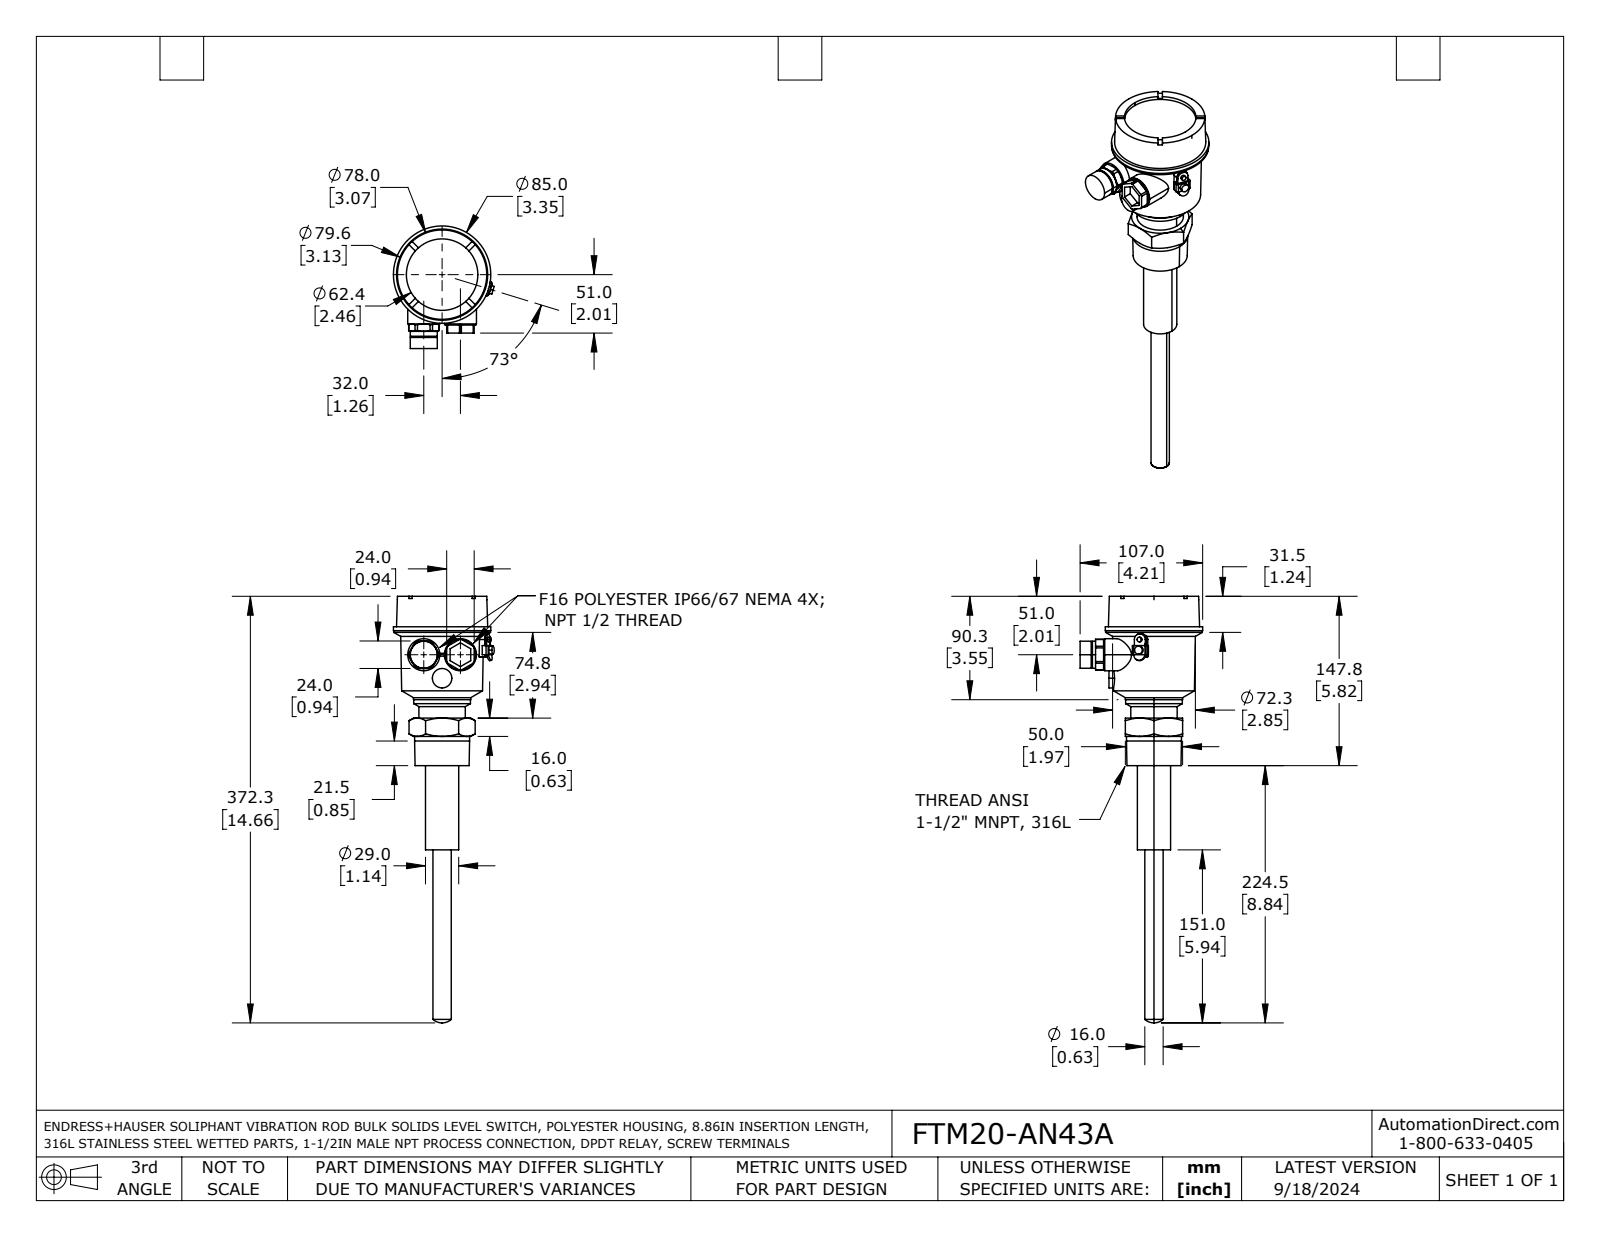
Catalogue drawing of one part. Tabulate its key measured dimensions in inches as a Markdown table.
| quantity | value |
| --- | --- |
| part name | FTM20-AN43A |
| STEP written by | SolidWorks 2021 (AUTOMOTIVE_DESIGN) |
| units | inches |
| bodies | 1 solid, 223 faces (113 planar, 56 cylindrical, 54 other) |
| overall size | 14.657 × 4.213 × 3.464 |
| volume | 35.84 in³ |
| surface area | 94.94 in² |
| round holes (diameter × count) | 2.457 × 1 |
| round bosses / shafts (diameter × count) | 1.102 × 2, 3.346 × 1, 3.327 × 1, 1.969 × 1, 1.949 × 1, 1.89 × 1, 1.594 × 1, 1.142 × 1 |
| partial cylindrical surfaces (radius × count) | 0.059 × 3, 0.197 × 1, 0.52 × 1 |
| main face-to-face distances | 0.118, 1.969, 5.701, 5.819, 4.772, 0.929, 1.047, 1.634, 3.138, 4.067 |
